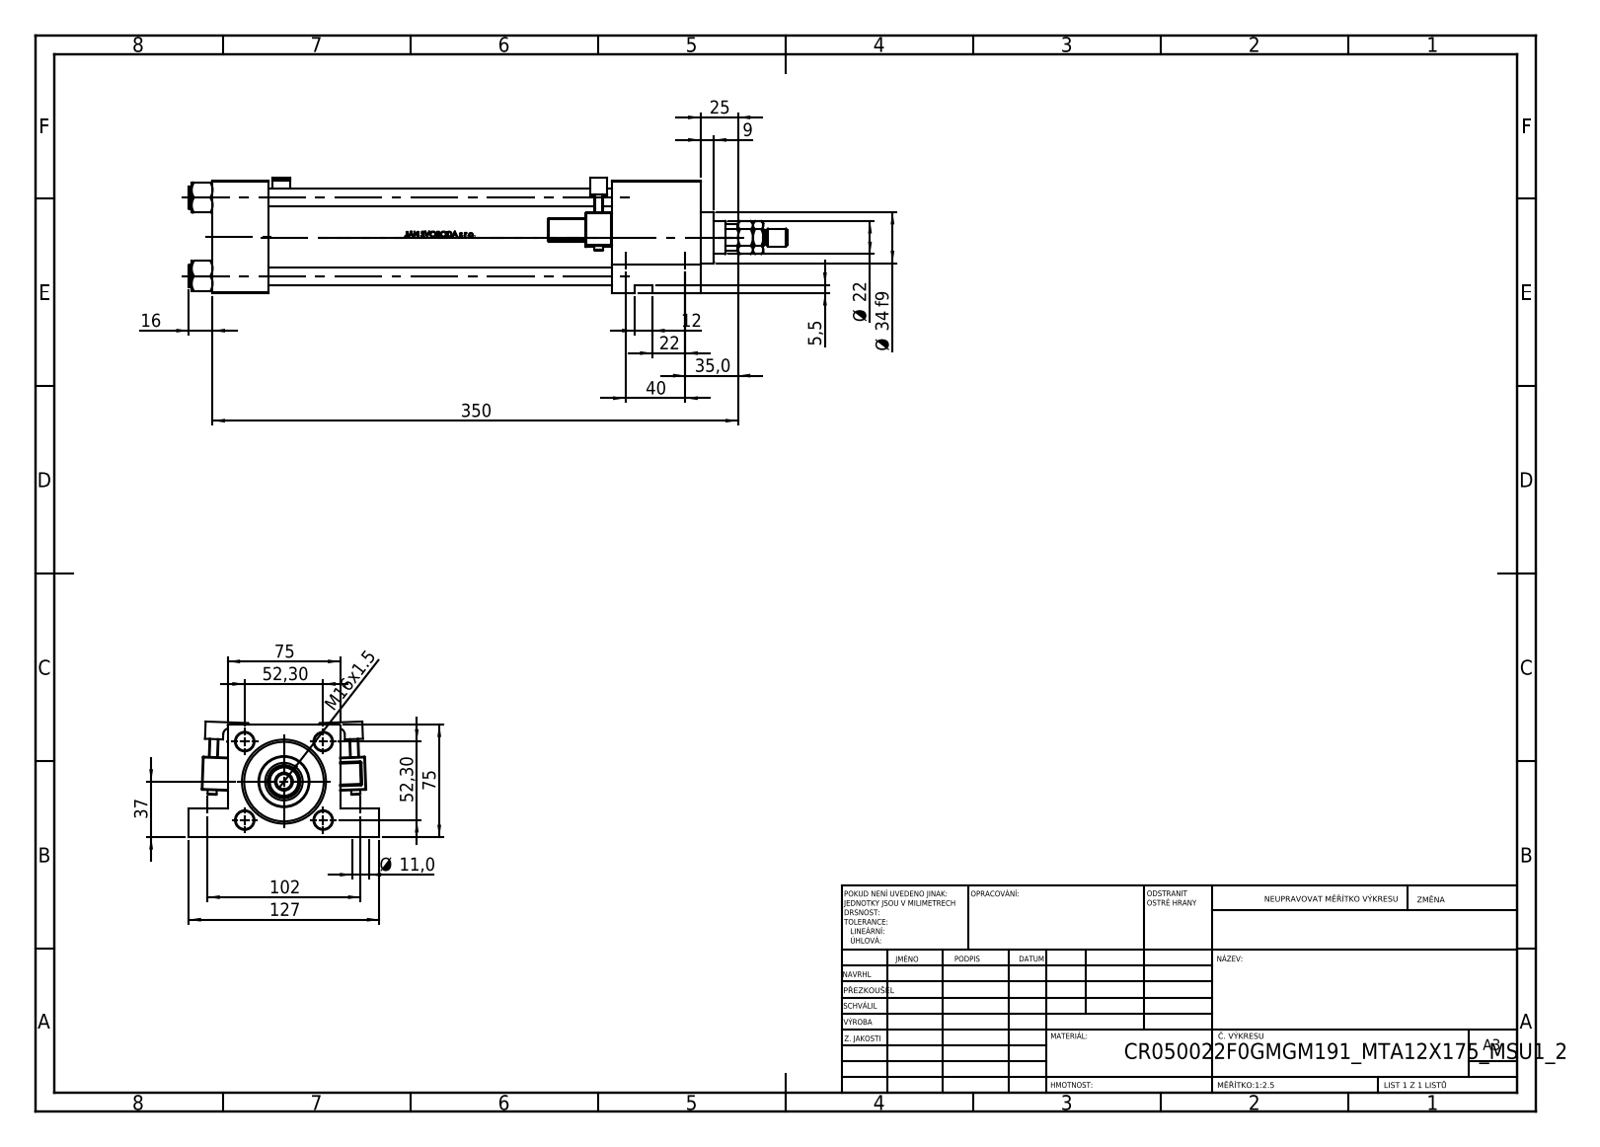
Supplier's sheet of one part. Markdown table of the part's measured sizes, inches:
| quantity | value |
| --- | --- |
| part name | V215CR_F_Body; V215CR_F_TYCINKA; MTA; V215_VC_A (+3 more) |
| STEP written by | SolidWorks 2019 (CONFIG_CONTROL_DESIGN) |
| units | inches |
| bodies | 14 solids, 1306 faces (510 planar, 190 cylindrical, 606 other) |
| overall size | 15.709 × 5 × 3.033 |
| volume | 59.96 in³ |
| surface area | 411.5 in² |
| round holes (diameter × count) | 0.433 × 4, 0.472 × 4, 0.276 × 2, 1.181 × 2, 0.413 × 1, 0.669 × 1, 0.825 × 1, 0.866 × 1, 0.984 × 1, 1.614 × 1, 1.969 × 1, 2.087 × 1 |
| round bosses / shafts (diameter × count) | 0.591 × 4, 0.236 × 2, 2.205 × 1, 1.339 × 1, 0.472 × 1, 0.394 × 1 |
| partial cylindrical surfaces (radius × count) | 0.02 × 48, 0.039 × 2, 0.098 × 2, 0.157 × 2, 0.413 × 1 |
| main face-to-face distances | 2.953, 1.457, 12.795, 11.339, 10.472, 9.016, 2.323, 0.748, 2.205, 11.665 |
| hole center spacings | 2.059, 1.442, 1.47, 1.575, 2.912, 4.016, 4.313, 10.413 |
